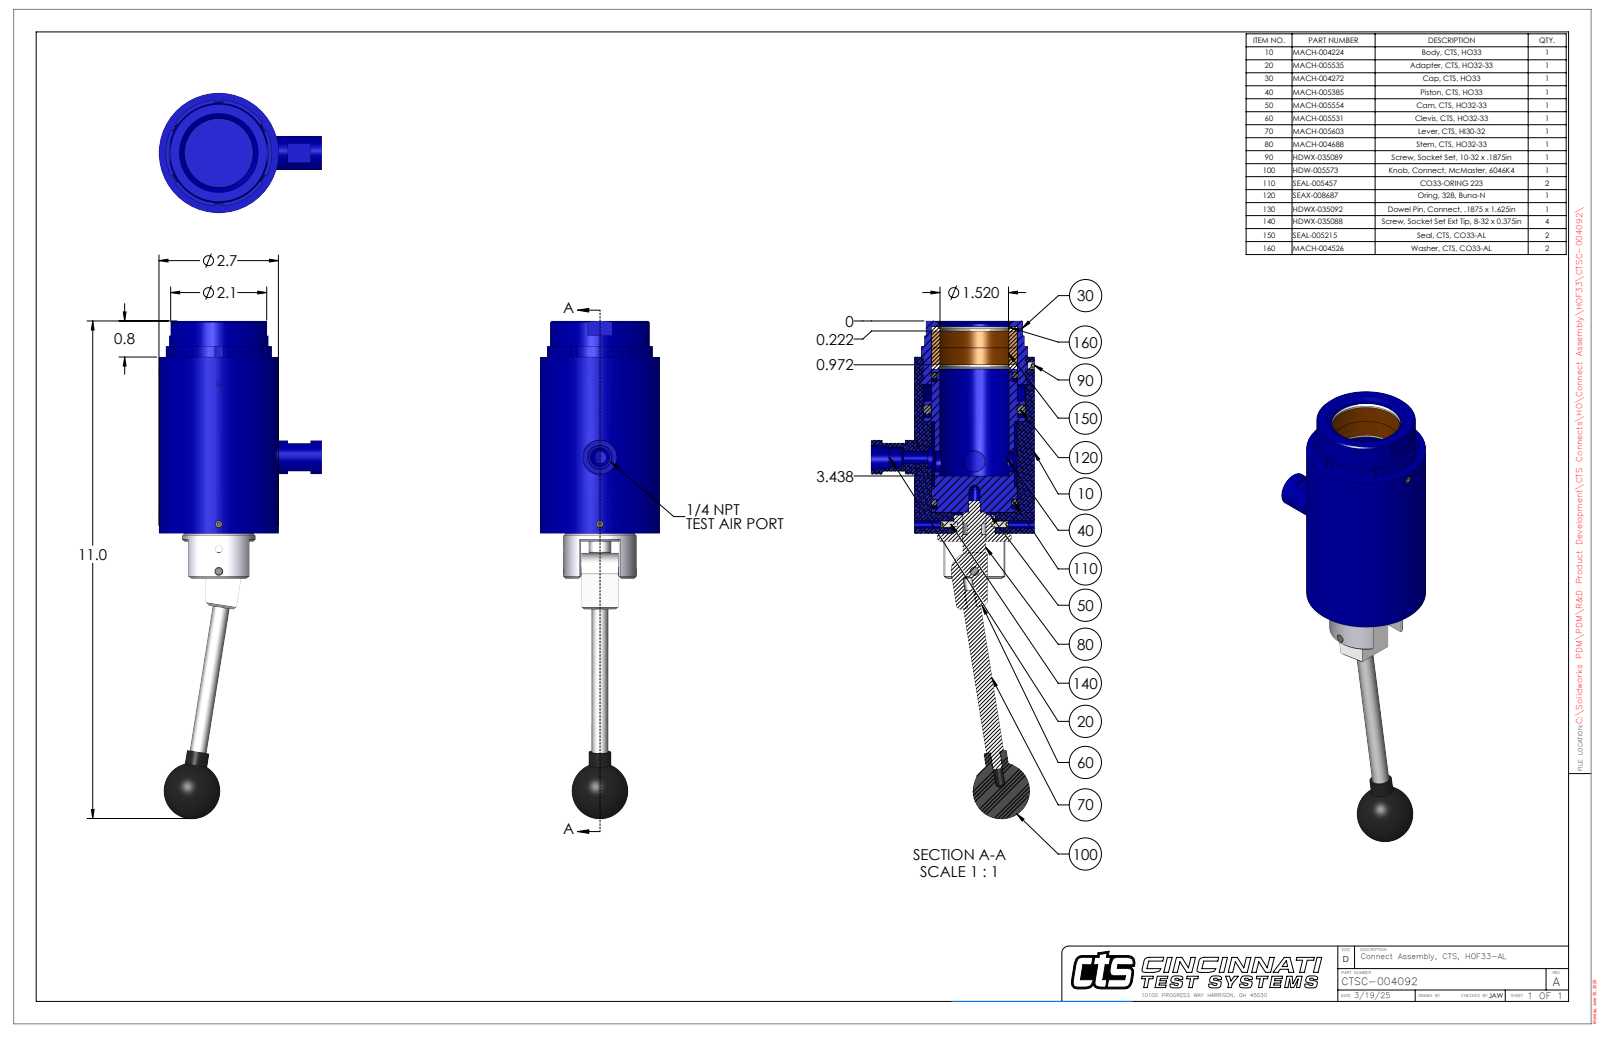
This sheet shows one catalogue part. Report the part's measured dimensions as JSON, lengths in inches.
{"part_name": "CTSC-004092", "step_written_by": "SolidWorks 2023 (AUTOMOTIVE_DESIGN)", "units": "inches", "bodies": {"solids": 15, "faces": 546, "planar": 179, "cylindrical": 226, "other": 141}, "overall_size": [11.035, 3.6, 2.65], "volume_in3": 21.33, "surface_area_in2": 133.2, "round_holes": [[0.201, 3], [0.159, 2], [0.469, 2], [0.094, 1], [0.189, 1], [0.19, 1], [0.25, 1], [0.281, 1], [0.438, 1], [0.5, 1], [0.516, 1], [0.533, 1]], "round_bosses_or_shafts": [[0.75, 2], [0.5, 2], [0.164, 2], [0.109, 2], [2.65, 1], [2.344, 1], [2.2, 1], [1.885, 1]], "partial_cylinders_radius": [[0.385, 1], [0.4, 1], [1.13, 1], [1.19, 1]], "face_to_face_distances": [0.844, 0.094, 0.75, 3.736, 4.486, 0.375, 0.375, 4.111, 1.27, 2.466], "hole_center_spacings": [0.093, 0.488, 1.713, 1.945, 2.033, 2.126, 2.433, 3.658]}
